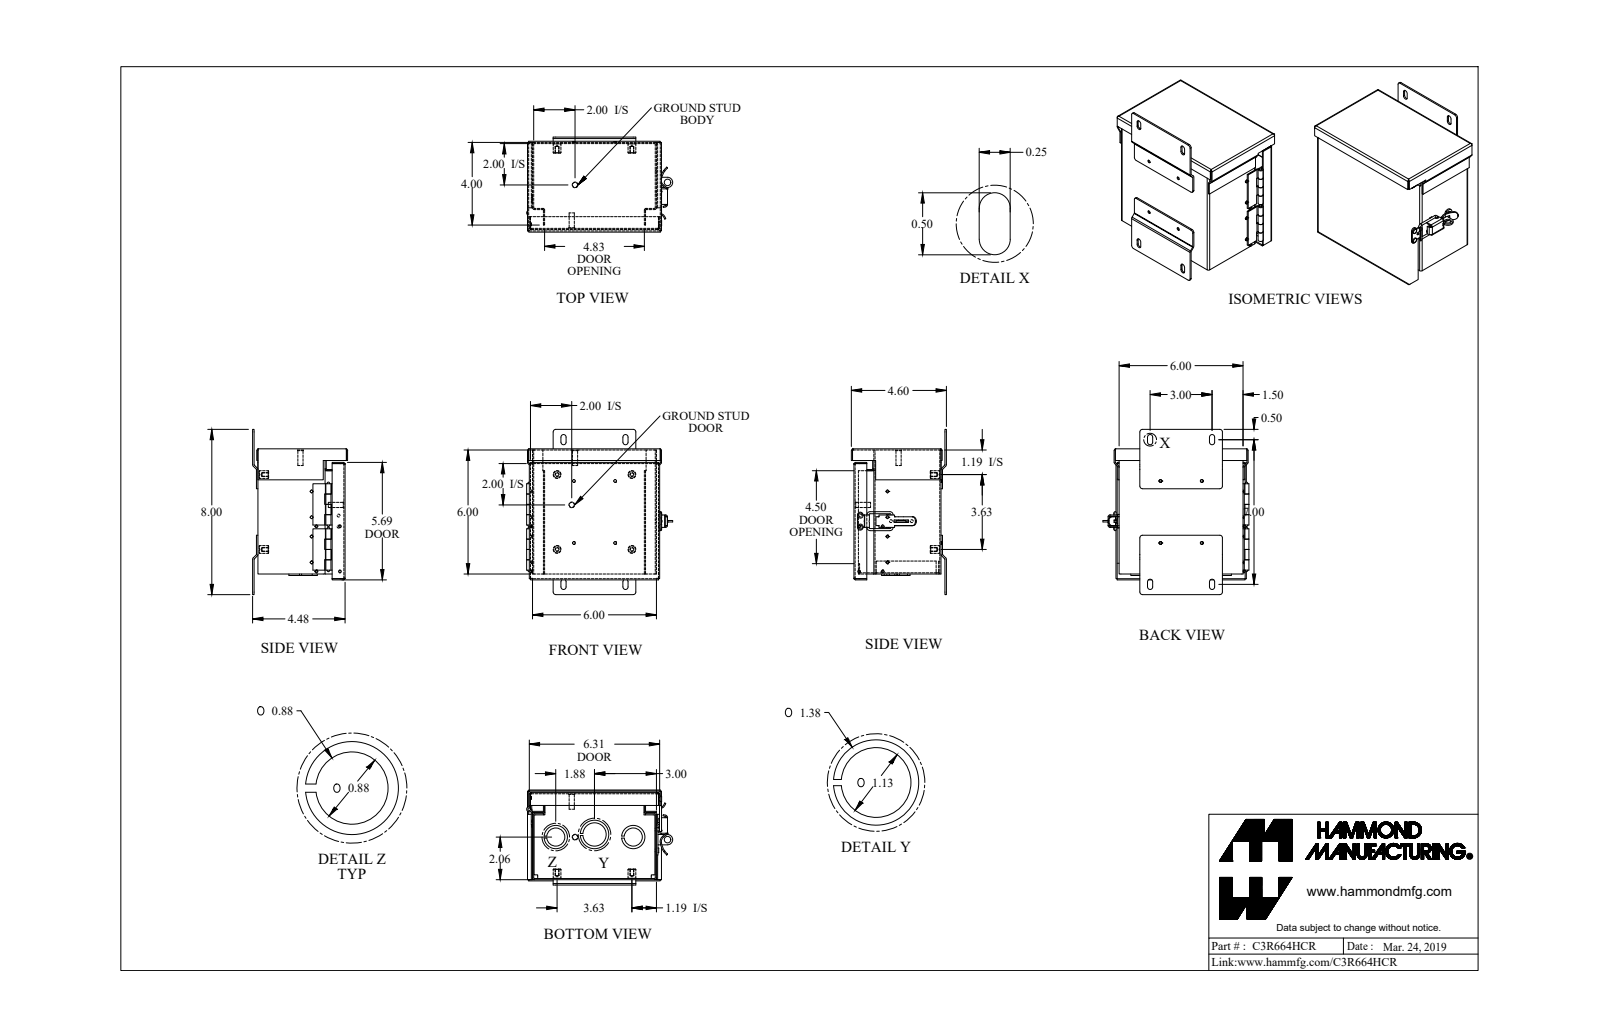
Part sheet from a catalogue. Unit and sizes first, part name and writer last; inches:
Units: inches
Overall size (bounding box): 8 × 7.07 × 4.599
Round holes (diameter × count): ⌀0.137 ×4, ⌀0.14 ×4, ⌀0.156 ×4, ⌀0.133 ×2, ⌀0.145 ×2, ⌀0.875 ×2, ⌀0.125 ×1, ⌀0.13 ×1, ⌀0.313 ×1, ⌀1.125 ×1
Round bosses / shafts (diameter × count): ⌀0.131 ×12, ⌀0.375 ×4, ⌀0.125 ×4, ⌀0.1 ×4, ⌀1.125 ×2, ⌀0.281 ×2, ⌀0.25 ×2, ⌀1.375 ×1
Partial cylindrical surfaces — rounded edges, fillets, slot ends (radius × count): R0.029 ×28, R0.086 ×28, R0.125 ×21, R0.036 ×6, R0.108 ×6, R0.135 ×2, R0.04 ×1, R0.067 ×1
Main face-to-face distances: 0.057, 4.16, 6, 5.943, 0.187, 4.103, 0.244, 4.217, 6.057, 5.886
Hole centre spacings: 3.625, 1.498, 1.01, 1.01, 2, 2.498, 2.829, 2.83
Volume: 18.45 in³ · Surface area: 581.1 in²
Bodies: 31 solids, 841 faces (493 planar, 293 cylindrical, 55 other)
Part name (STEP PRODUCT): C3R664HCR_Default
STEP written by: SolidWorks 2019 (CONFIG_CONTROL_DESIGN)
